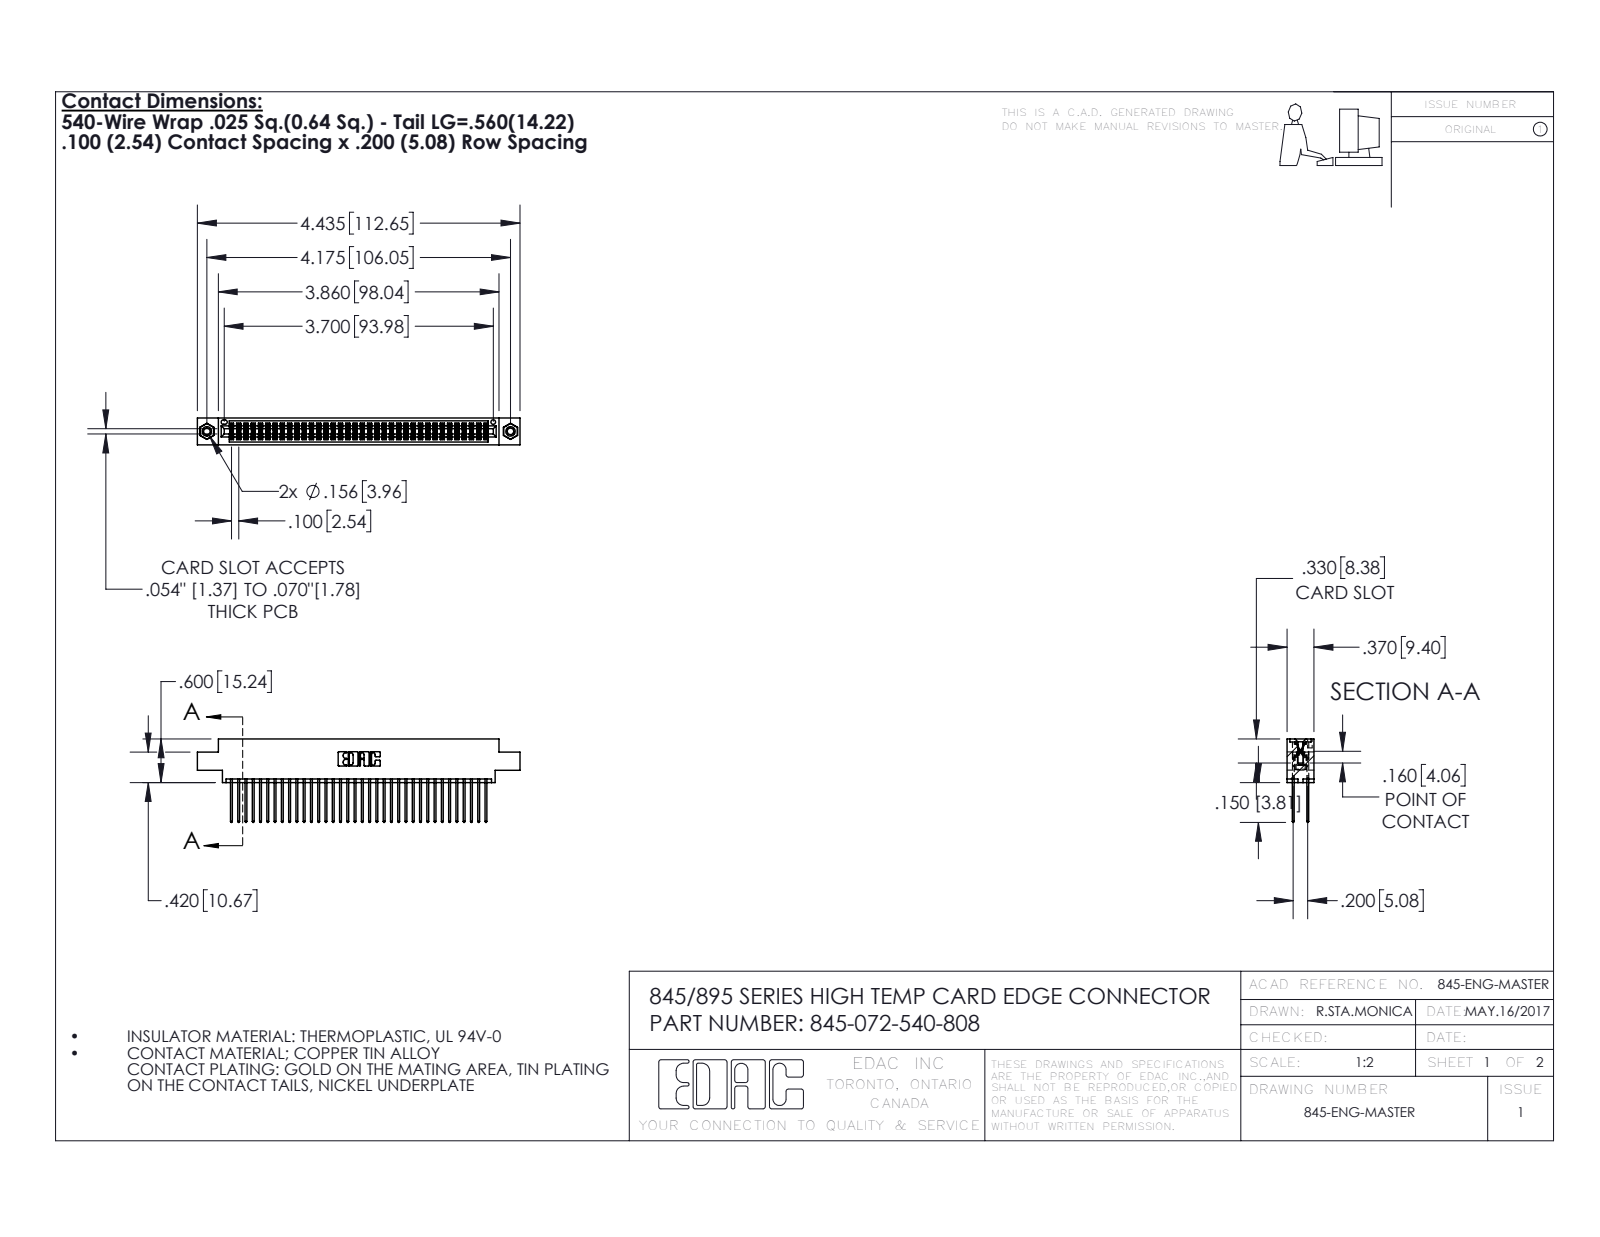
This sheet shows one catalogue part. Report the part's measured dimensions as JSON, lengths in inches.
{"part_name": "345-250-001_345-250-003-102; 345-292-001_345-293-140; 345-072-540-808; 345 Part_0.170 Offset - 0.156 Dia-TI", "step_written_by": "SolidWorks 2016 (CONFIG_CONTROL_DESIGN)", "units": "inches", "bodies": {"solids": 75, "faces": 3790, "planar": 2492, "cylindrical": 1282, "other": 16}, "overall_size": [4.435, 1.147, 0.37], "volume_in3": 0.674, "surface_area_in2": 27.32, "round_holes": [[0.089, 2], [0.125, 2], [0.156, 2], [0.064, 1]], "round_bosses_or_shafts": [[0.155, 2]], "partial_cylinders_radius": [[0.006, 109], [0.01, 72], [0.01, 22], [0.007, 6], [0.031, 6], [0.026, 3], [0.014, 2], [0.019, 2]], "face_to_face_distances": [0.072, 0.298, 0.2, 0.098, 0.272, 0.025, 0.37, 0.225, 0.175, 0.149], "hole_center_spacings": [0.27, 3.939, 4.175]}
